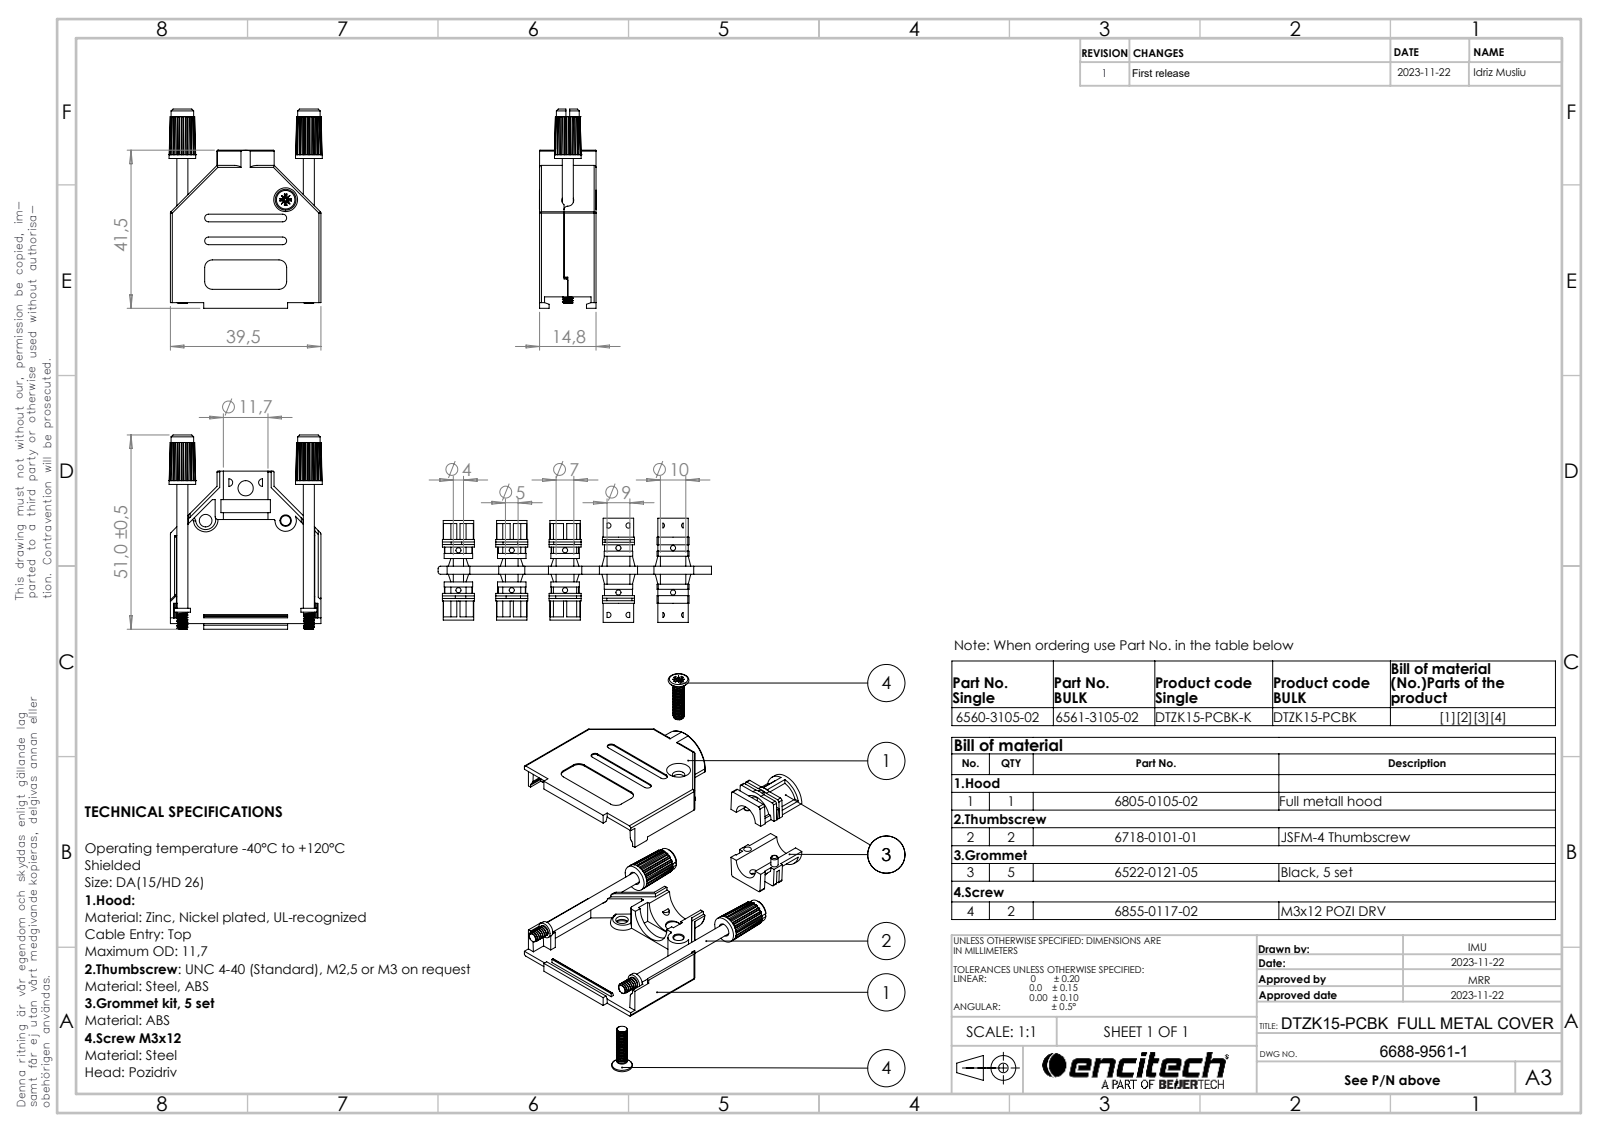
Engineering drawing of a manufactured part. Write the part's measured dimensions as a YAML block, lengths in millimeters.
part_name: "6855-0117-02; 6522-0121-05 (7mm); 6688-9561-1; 6718-0101-01 (+1 more)"
step_written_by: "SolidWorks 2021 (AUTOMOTIVE_DESIGN)"
units: millimeters
bodies: {solids: 8, faces: 868, planar: 506, cylindrical: 256, other: 106}
overall_size: [52.3, 40.2, 14.85]
volume: 8294
surface_area: 12448
round_holes:
  - {diameter: 2, count: 3}
  - {diameter: 2.6, count: 2}
  - {diameter: 3.3, count: 2}
  - {diameter: 4, count: 1}
  - {diameter: 7, count: 1}
  - {diameter: 11.7, count: 1}
round_bosses_or_shafts:
  - {diameter: 2.9, count: 4}
  - {diameter: 7, count: 2}
  - {diameter: 6, count: 2}
  - {diameter: 4.2, count: 2}
  - {diameter: 1.9, count: 2}
  - {diameter: 15, count: 1}
  - {diameter: 11.6, count: 1}
  - {diameter: 9.2, count: 1}
partial_cylinders:
  - {radius: 0.5, count: 24}
  - {radius: 1, count: 12}
  - {radius: 0.1, count: 8}
  - {radius: 0.25, count: 8}
  - {radius: 0.2, count: 6}
  - {radius: 0.3, count: 4}
  - {radius: 1.55, count: 4}
  - {radius: 2, count: 4}
face_to_face_distances: [1.3, 13.5, 14.8, 12.2, 6.1, 7.4, 1, 7.1, 1.6, 14.5]
hole_center_spacings: [5.71, 6.6, 6.97, 10.54, 13.51, 15.92, 7.6, 10]
